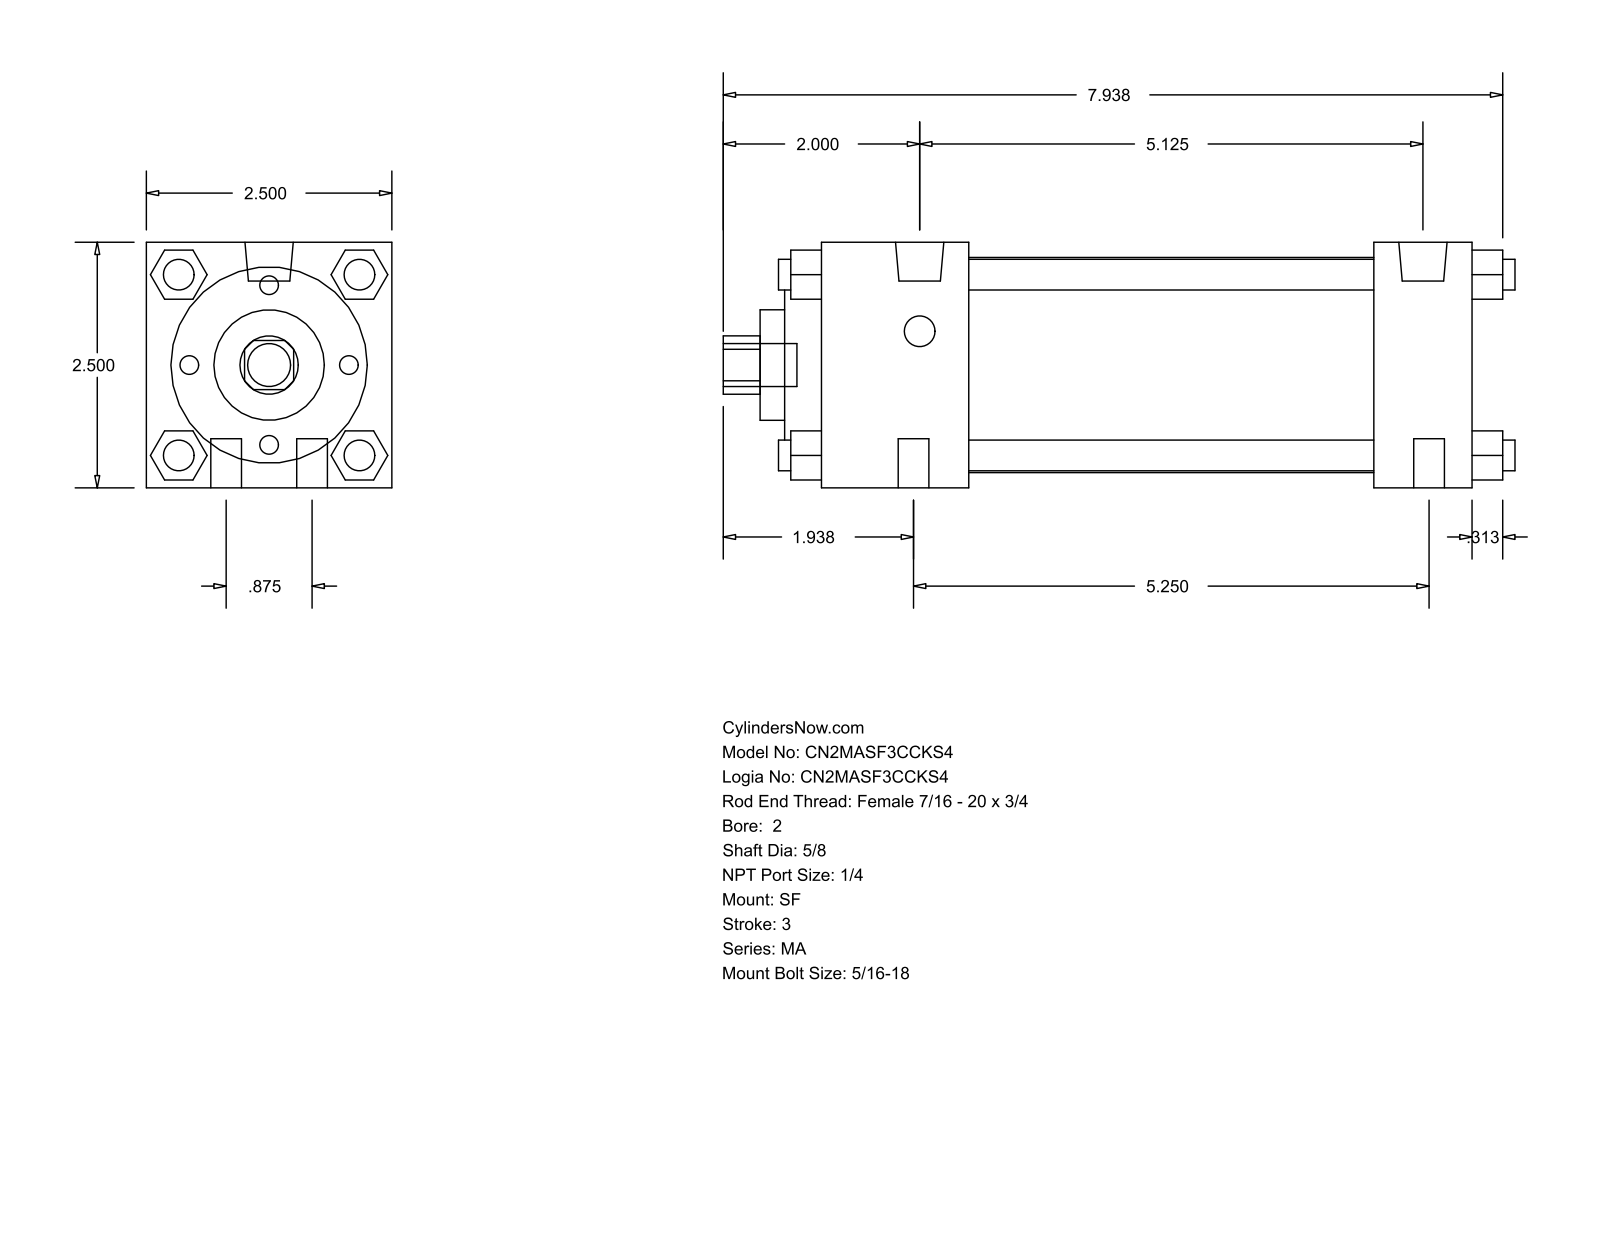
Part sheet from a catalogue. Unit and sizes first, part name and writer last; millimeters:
Units: millimetres
Overall size (bounding box): 204.79 × 63.5 × 63.5
Round holes (diameter × count): ⌀15.88 ×1, ⌀28.57 ×1, ⌀50.8 ×1, ⌀55.63 ×1
Round bosses / shafts (diameter × count): ⌀7.94 ×10, ⌀12.49 ×2, ⌀11.11 ×1
Partial cylindrical surfaces — rounded edges, fillets, slot ends (radius × count): R7.54 ×1
Main face-to-face distances: 63.5, 12.7, 25.4, 38.1, 168.28, 9.52, 142.88, 104.78, 130.18, 47.62
Bodies: 0 solids, 126 faces (95 planar, 31 cylindrical, 0 other)
Part name (STEP PRODUCT): MA_SF__0200_0.625
STEP written by: GSSL Pune (CONFIG_CONTROL_DESIGN)
